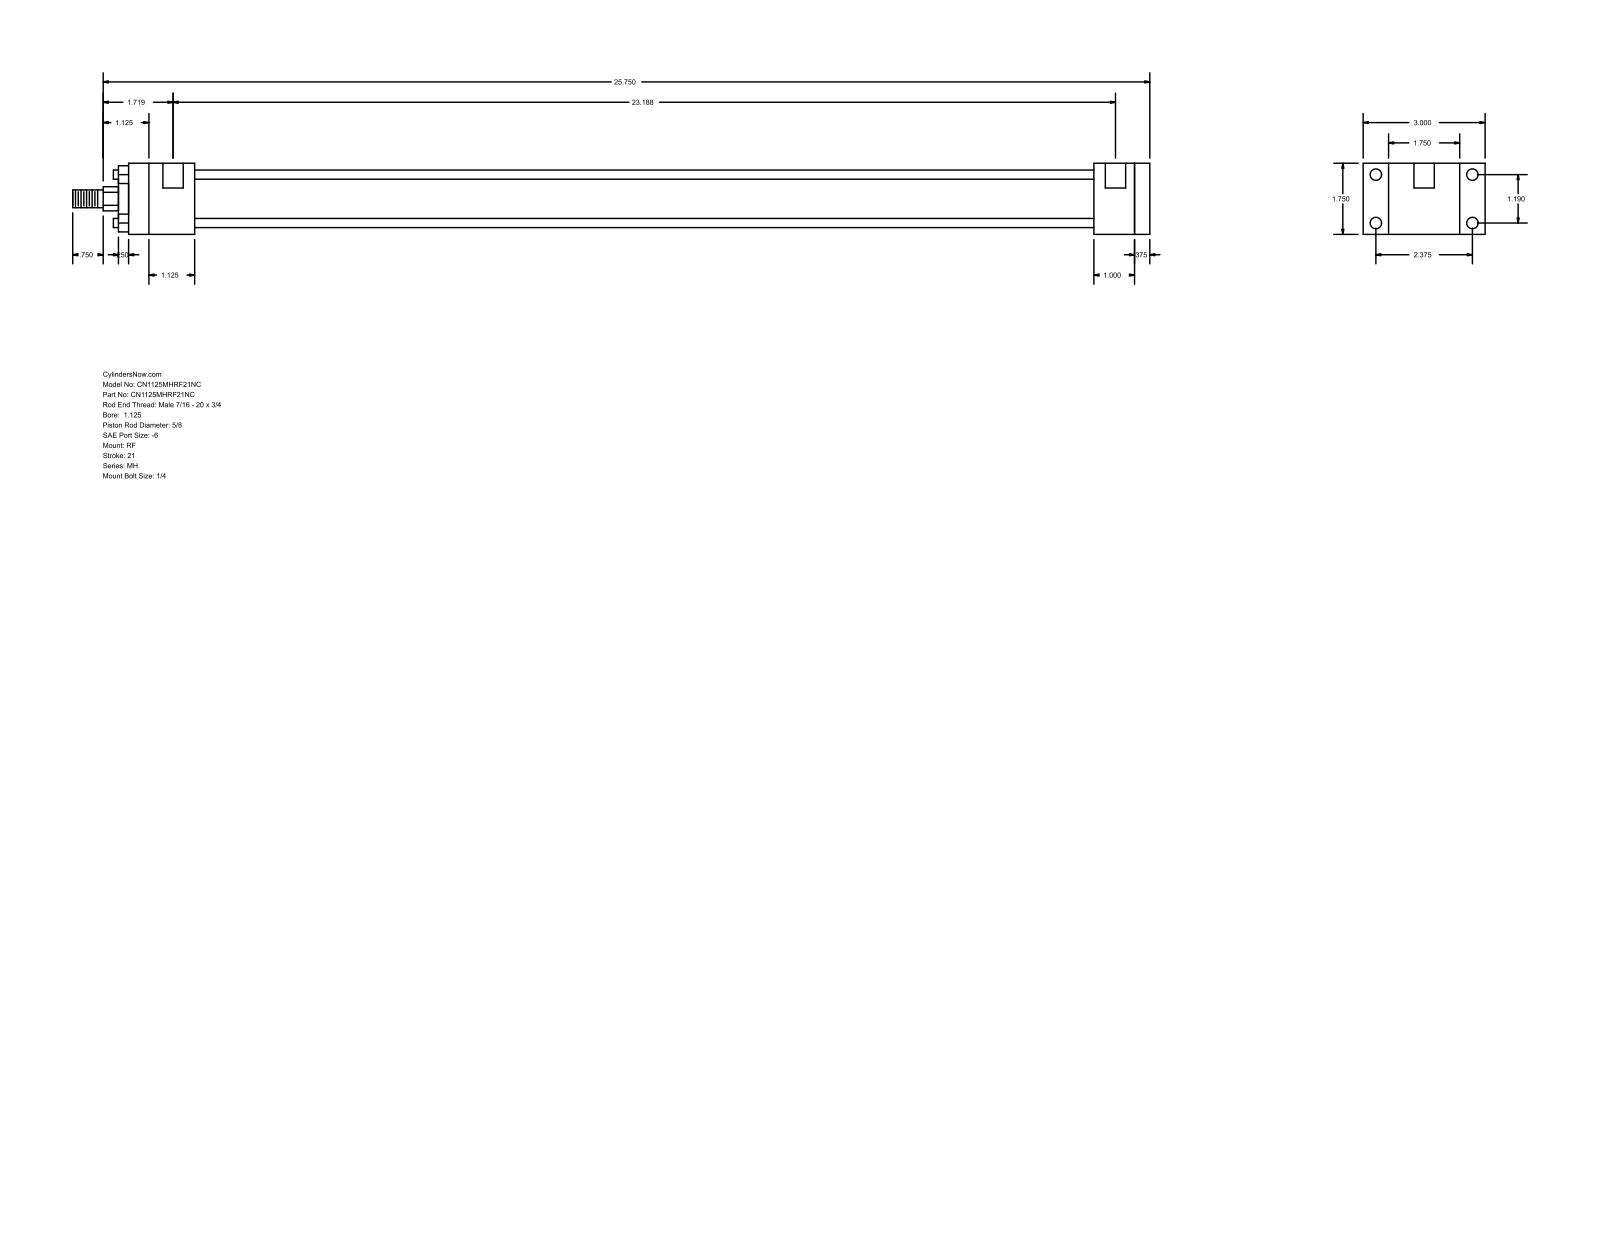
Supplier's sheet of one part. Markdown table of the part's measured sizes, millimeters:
| quantity | value |
| --- | --- |
| part name | MH_RF__0112_0.625 |
| STEP written by | GSSL Pune (CONFIG_CONTROL_DESIGN) |
| units | millimeters |
| bodies | 0 solids, 92 faces (64 planar, 28 cylindrical, 0 other) |
| overall size | 673.1 × 76.2 × 44.45 |
| round holes (diameter × count) | 5.56 × 4, 7.14 × 4, 12.7 × 2 |
| round bosses / shafts (diameter × count) | 5.71 × 4, 34.92 × 1, 28.57 × 1, 15.88 × 1, 11.11 × 1 |
| partial cylindrical surfaces (radius × count) | 7.54 × 1 |
| main face-to-face distances | 44.46, 9.53, 638.17, 25.4, 34.93, 15.87, 587.37, 596.9, 561.97, 41.27 |
| hole center spacings | 30.22, 60.32, 67.47, 585.79, 3.17, 588.96 |
